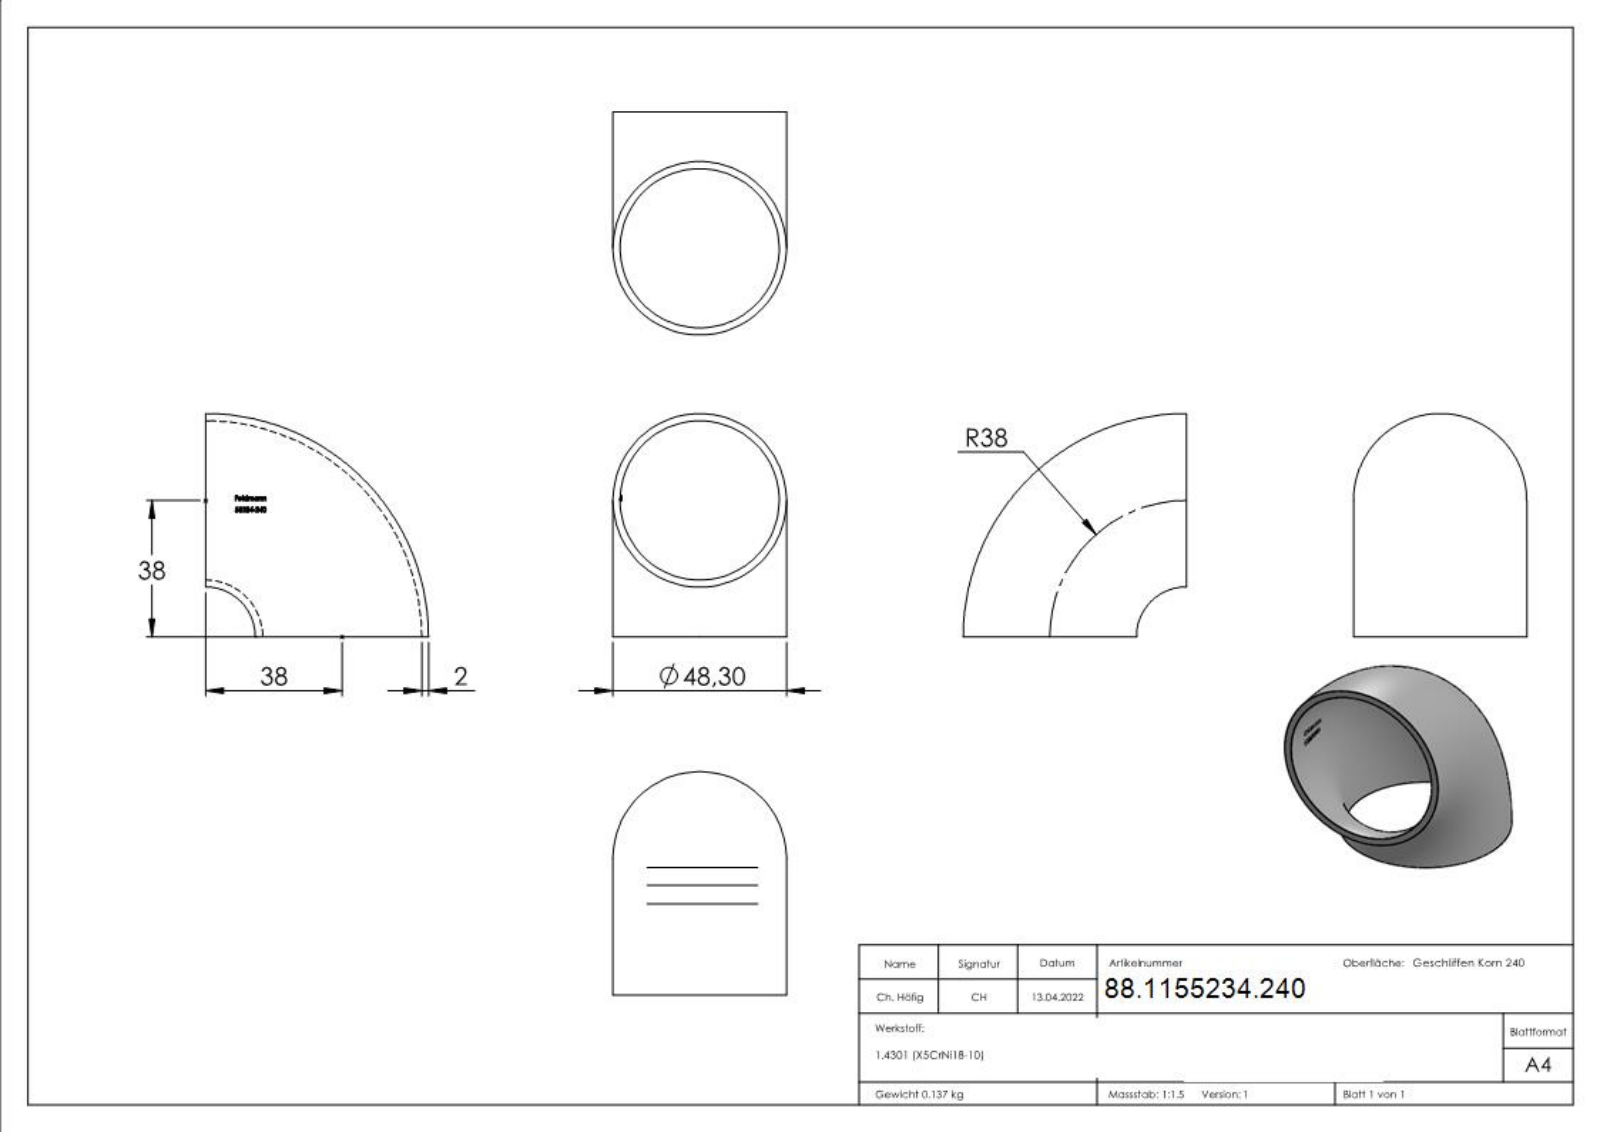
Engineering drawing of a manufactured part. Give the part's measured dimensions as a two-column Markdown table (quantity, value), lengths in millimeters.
| quantity | value |
| --- | --- |
| part name | 55234-240 |
| STEP written by | SolidWorks 2018 (CONFIG_CONTROL_DESIGN) |
| units | millimeters |
| bodies | 1 solid, 237 faces (113 planar, 0 cylindrical, 124 other) |
| overall size | 62.15 × 62.15 × 48.3 |
| volume | 17 364 mm³ |
| surface area | 17 956 mm² |
| main face-to-face distances | 2.97, 1.32, 1.26, 0.33, 2.65, 0.39, 1.38, 3.66, 0.88, 3.27 |
